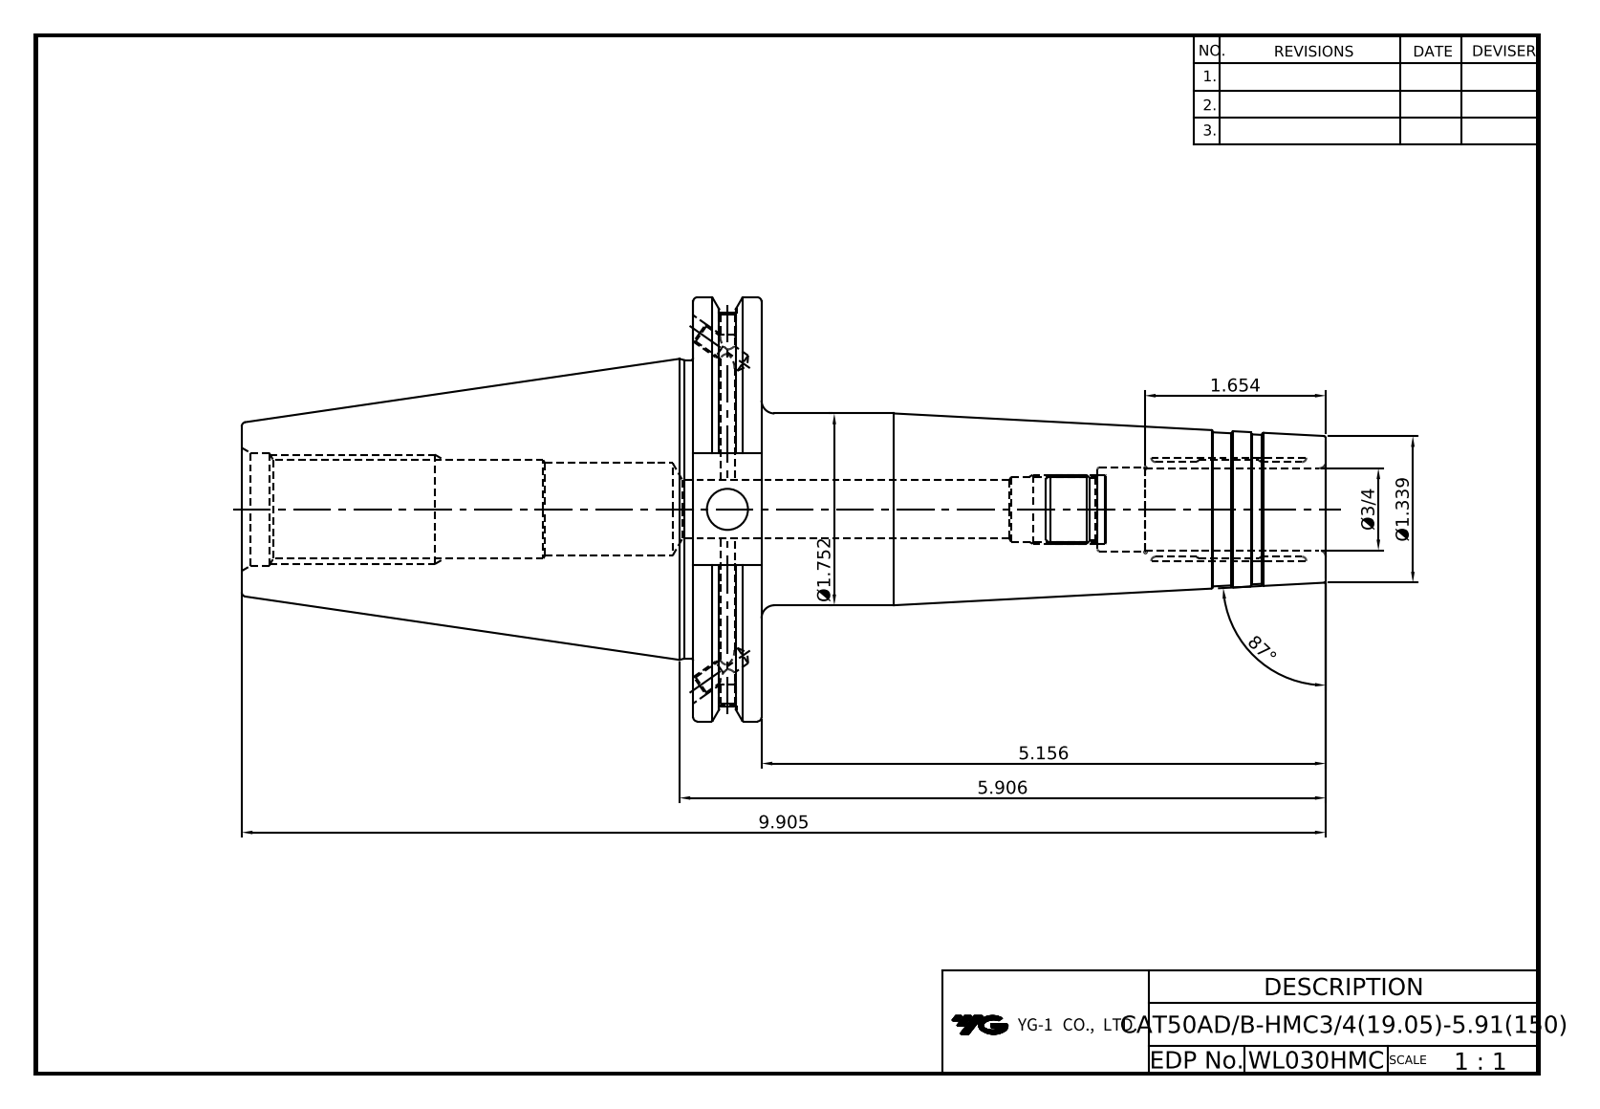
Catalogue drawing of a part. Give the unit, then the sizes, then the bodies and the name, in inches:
Units: inches
Overall size (bounding box): 9.906 × 3.875 × 3.728
Round holes (diameter × count): ⌀0.128 ×2, ⌀0.163 ×2, ⌀0.165 ×2, ⌀0.197 ×2, ⌀0.375 ×1, ⌀0.531 ×1, ⌀0.587 ×1, ⌀0.75 ×1, ⌀0.764 ×1, ⌀0.846 ×1, ⌀0.865 ×1, ⌀1.031 ×1
Round bosses / shafts (diameter × count): ⌀3.875 ×1, ⌀3.594 ×1, ⌀2.726 ×1, ⌀1.752 ×1
Main face-to-face distances: 0.625, 5.781, 5.156, 4.125, 4.75, 9.906, 2.875, 1.02, 4.363, 0.238
Volume: 28.42 in³ · Surface area: 103.9 in²
Bodies: 1 solid, 104 faces (37 planar, 28 cylindrical, 39 other)
Part name (STEP PRODUCT): LO-CAT50ADB-HMC19.05-150
STEP written by: Autodesk Inventor 2020 (AUTOMOTIVE_DESIGN)
